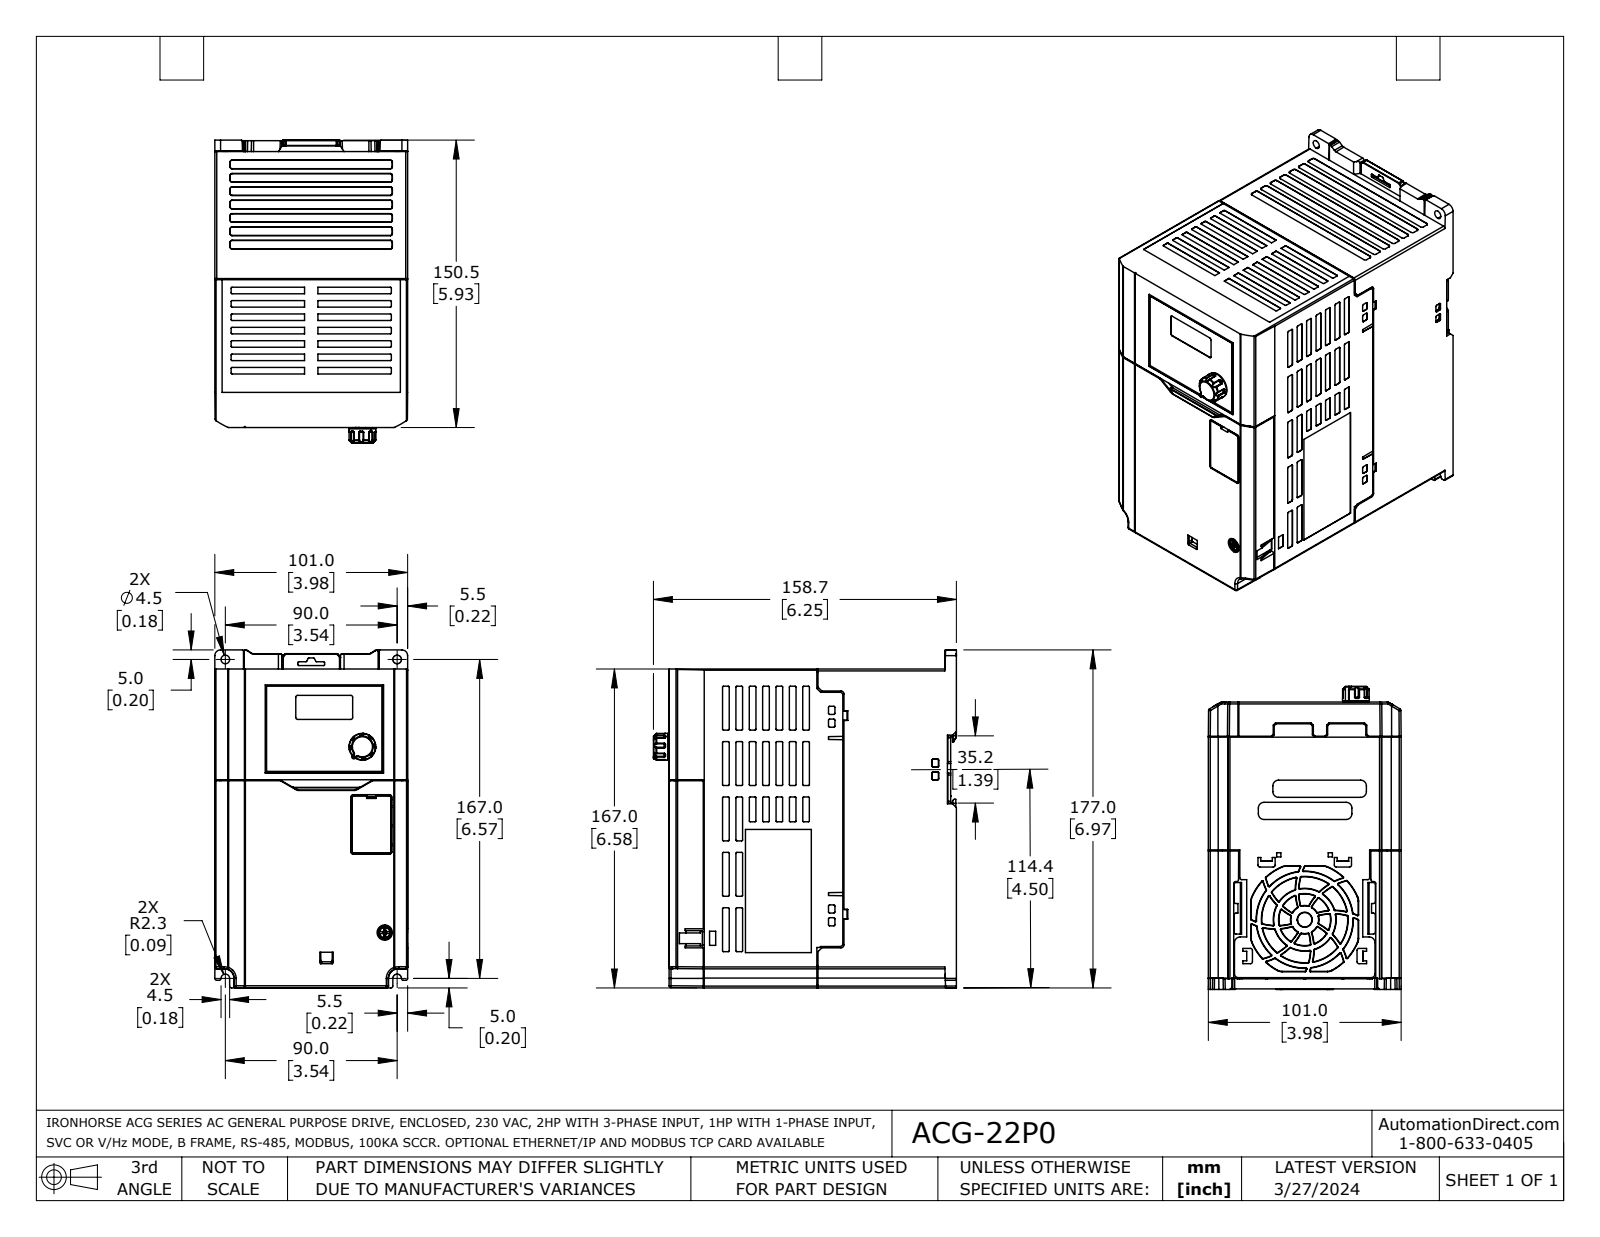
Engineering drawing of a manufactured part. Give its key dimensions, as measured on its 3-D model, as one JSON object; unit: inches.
{"part_name": "ACG-22P0", "step_written_by": "SolidWorks 2021 (AUTOMOTIVE_DESIGN)", "units": "inches", "bodies": {"solids": 4, "faces": 4588, "planar": 1880, "cylindrical": 1198, "other": 1510}, "overall_size": [6.969, 6.248, 3.976], "volume_in3": 150.5, "surface_area_in2": 234.5, "round_holes": [[0.134, 4], [0.039, 1], [0.276, 1], [0.472, 1]], "round_bosses_or_shafts": [[0.551, 1], [0.543, 1], [0.236, 1]], "partial_cylinders_radius": [[0.008, 347], [0.02, 240], [0.039, 95], [0.018, 38], [0.012, 24], [0.031, 17], [0.118, 12], [0.016, 4]], "face_to_face_distances": [3.976, 5.807, 3.975, 6.575, 5.795, 6.573, 0.106, 5.913, 0.118, 0.098], "hole_center_spacings": [3.496, 4.882, 6.005, 0.276, 0.491, 0.928, 1.202, 2.754]}
